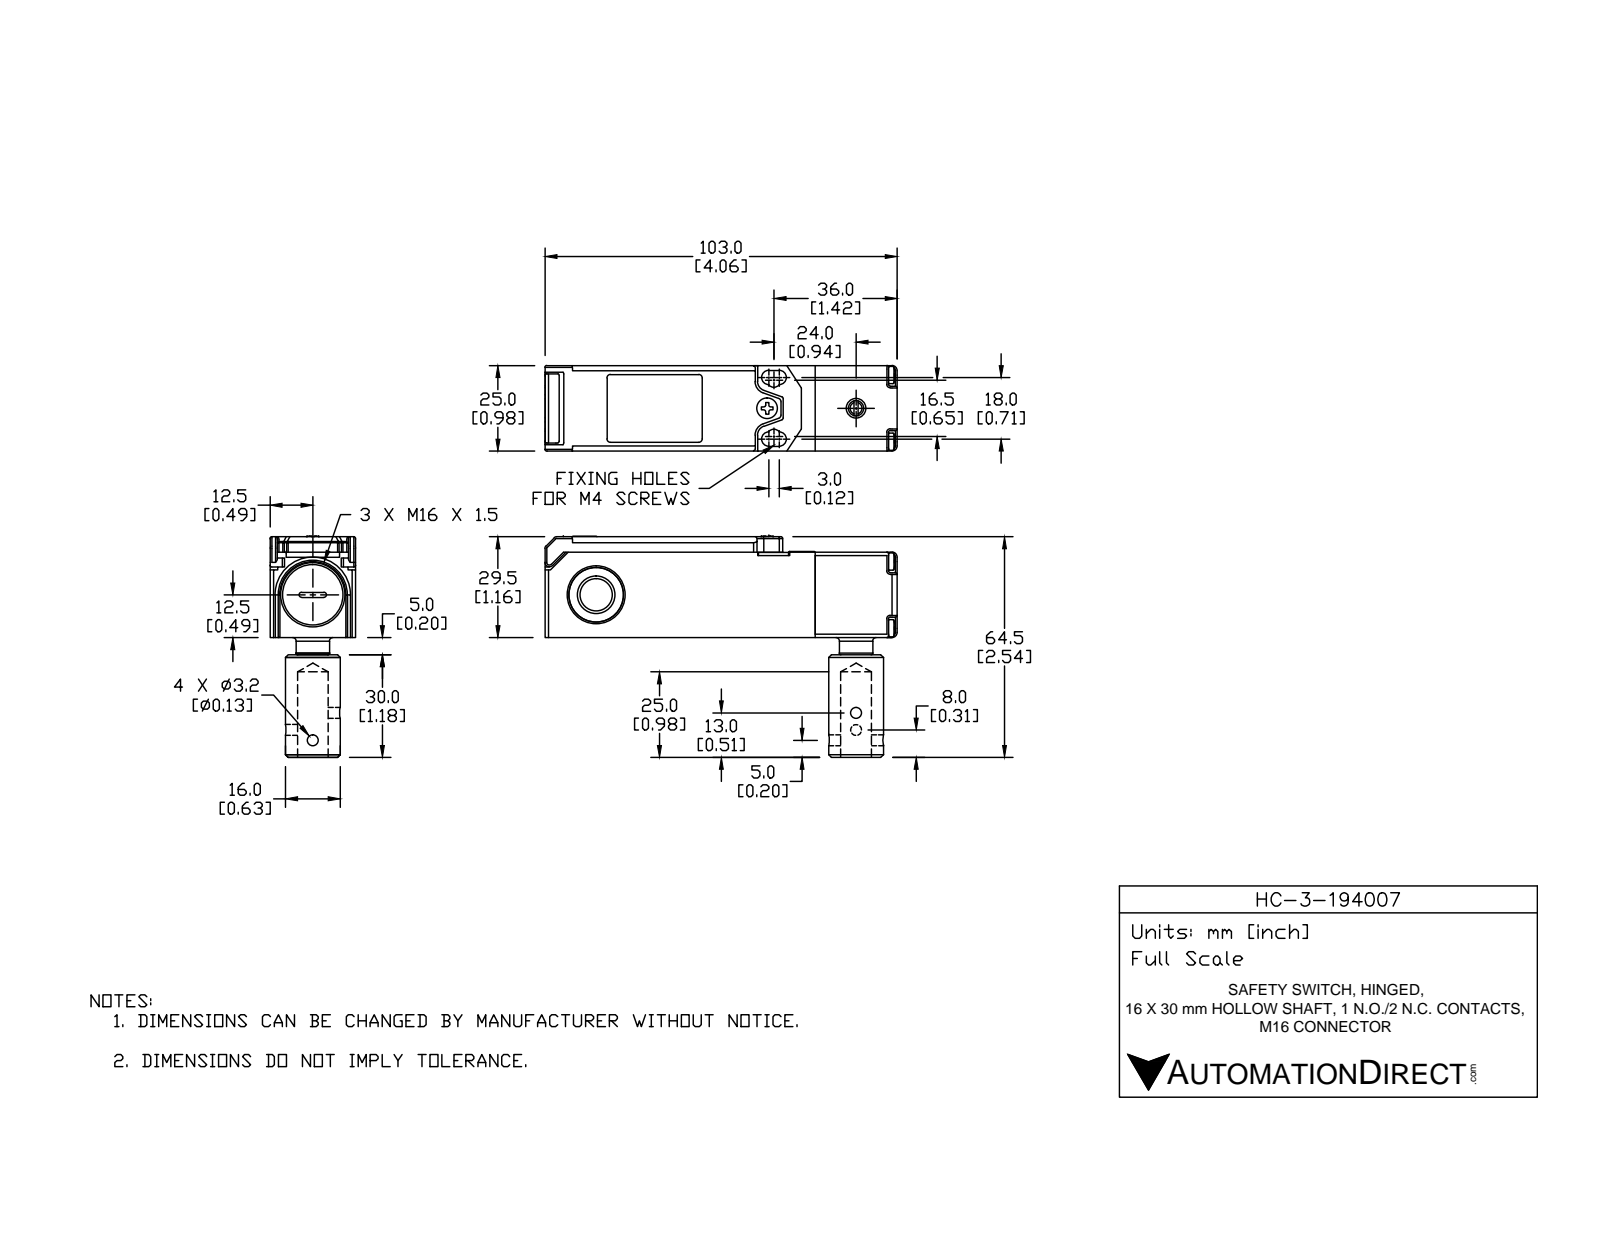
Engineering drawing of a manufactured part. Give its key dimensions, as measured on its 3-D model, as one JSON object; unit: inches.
{"part_name": "HC-3-194007", "step_written_by": "SolidWorks 2014 (AUTOMOTIVE_DESIGN)", "units": "inches", "bodies": {"solids": 13, "faces": 1862, "planar": 866, "cylindrical": 593, "other": 403}, "overall_size": [4.055, 2.549, 0.984], "volume_in3": 2.095, "surface_area_in2": 52.91, "round_holes": [[0.126, 8], [0.094, 4], [0.059, 2], [0.063, 2], [0.071, 2], [0.087, 2], [0.142, 2], [0.63, 2], [0.055, 1], [0.081, 1], [0.098, 1], [0.102, 1]], "round_bosses_or_shafts": [[0.102, 5], [0.197, 4], [0.079, 4], [0.138, 2], [0.63, 1], [0.386, 1], [0.256, 1], [0.228, 1]], "partial_cylinders_radius": [[0.02, 225], [0.004, 24], [0.039, 21], [0.012, 12], [0.059, 6], [0.083, 6], [0.11, 6], [0.138, 6]], "face_to_face_distances": [0.984, 0.079, 0.071, 0.913, 0.177, 0.906, 0.098, 0.039, 0.827, 0.087], "hole_center_spacings": [0.543, 0.768, 0.171, 0.187, 0.245, 0.414, 0.423, 0.426]}
